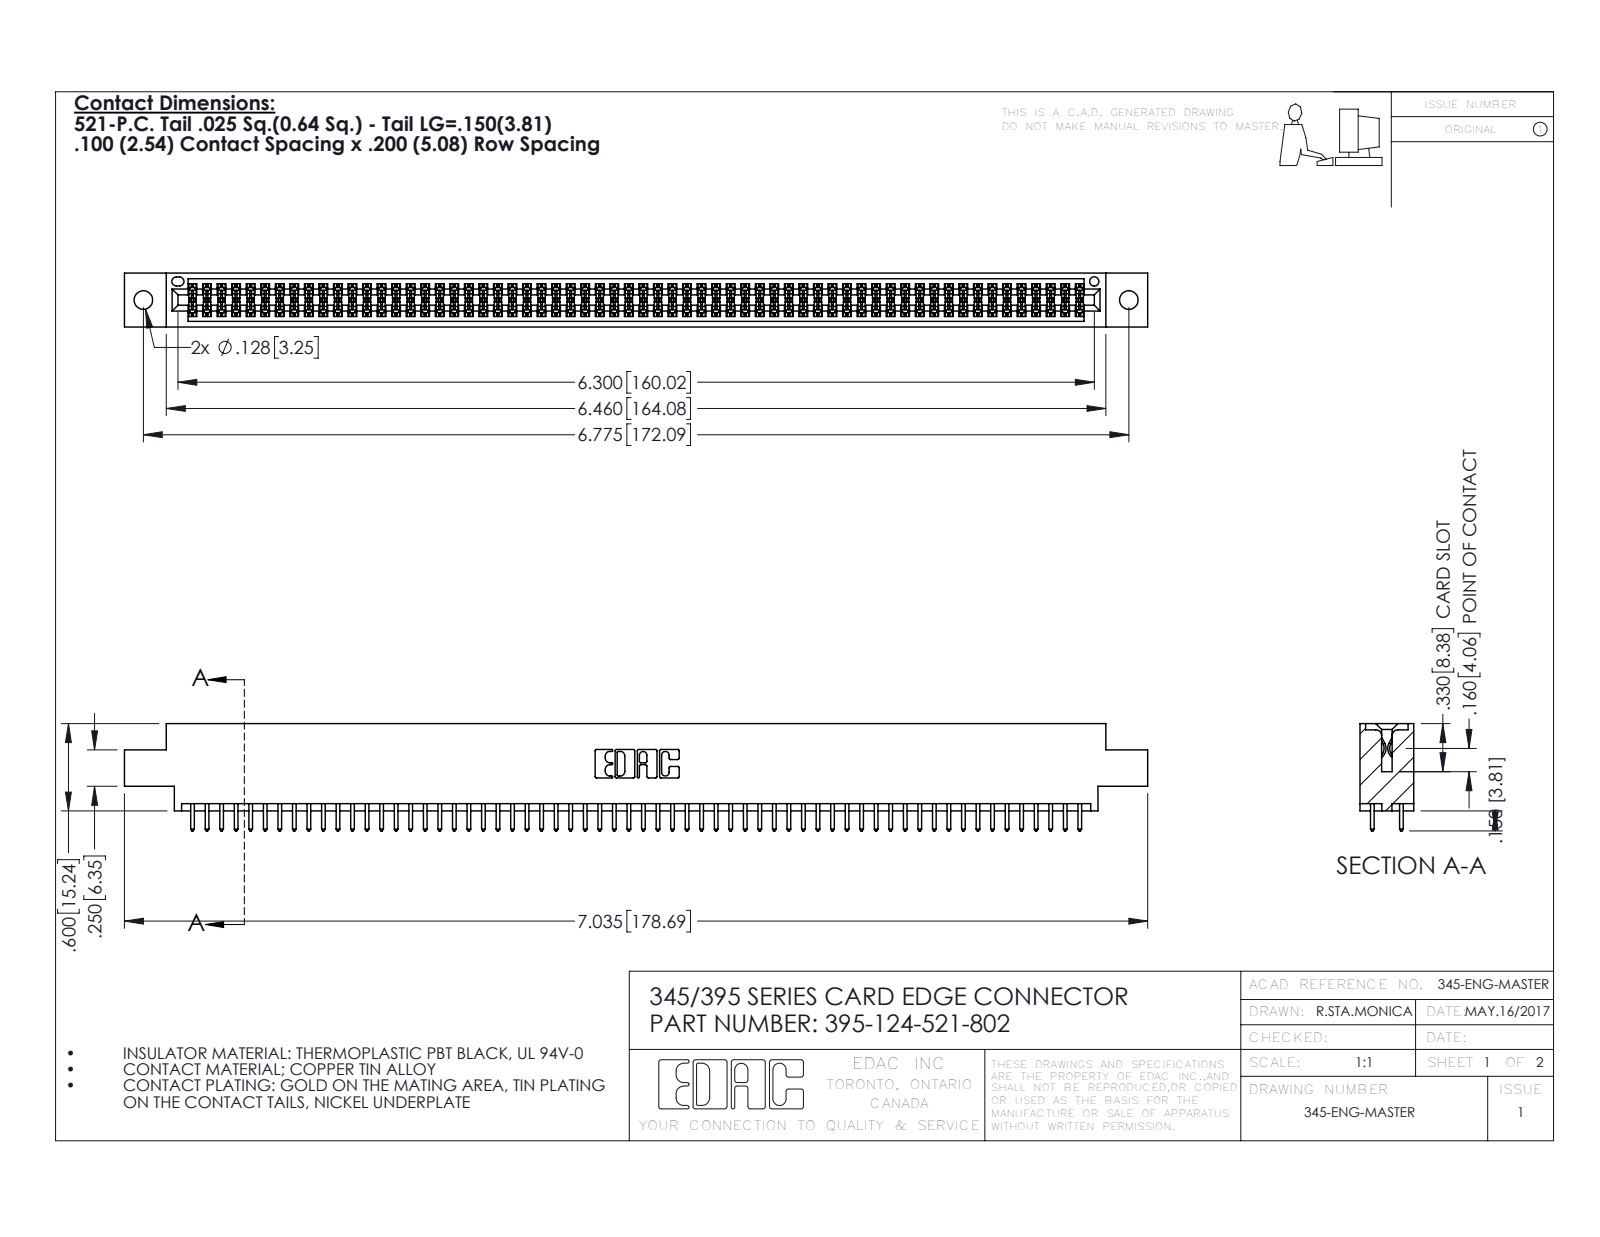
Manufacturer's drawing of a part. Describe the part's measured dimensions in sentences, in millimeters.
The part is named "345-292-001_345-293-121; 395-124-521-802; 345 Part_0.170 Offset - 0.128 Dia". Its 3-D file was written by "SolidWorks 2016 (CONFIG_CONTROL_DESIGN)". It is 125 solids with 6330 faces: 4176 planar, 2154 cylindrical and 0 other. Overall it measures 178.7 by 18.7 by 9.4 millimeters. Its volume is 17 340 cubic millimeters and its surface area 25 570 square millimeters. Round holes: 2 of diameter 3.3, 1 of diameter 1.6. Partial cylindrical surfaces (rounded edges, fillets, slot ends): 186 of radius 0.2, 124 of radius 0.3, 22 of radius 0.3, 6 of radius 0.2, 6 of radius 0.8, 3 of radius 0.7, 2 of radius 0.4, 2 of radius 0.5. The main face-to-face distances are 1.8, 7.6, 5.1, 9.4, 2.5, 6.9, 0.6, 5.7, 4.4, 3.8. The hole center spacings are 6.9, 166.1, 172.1.
